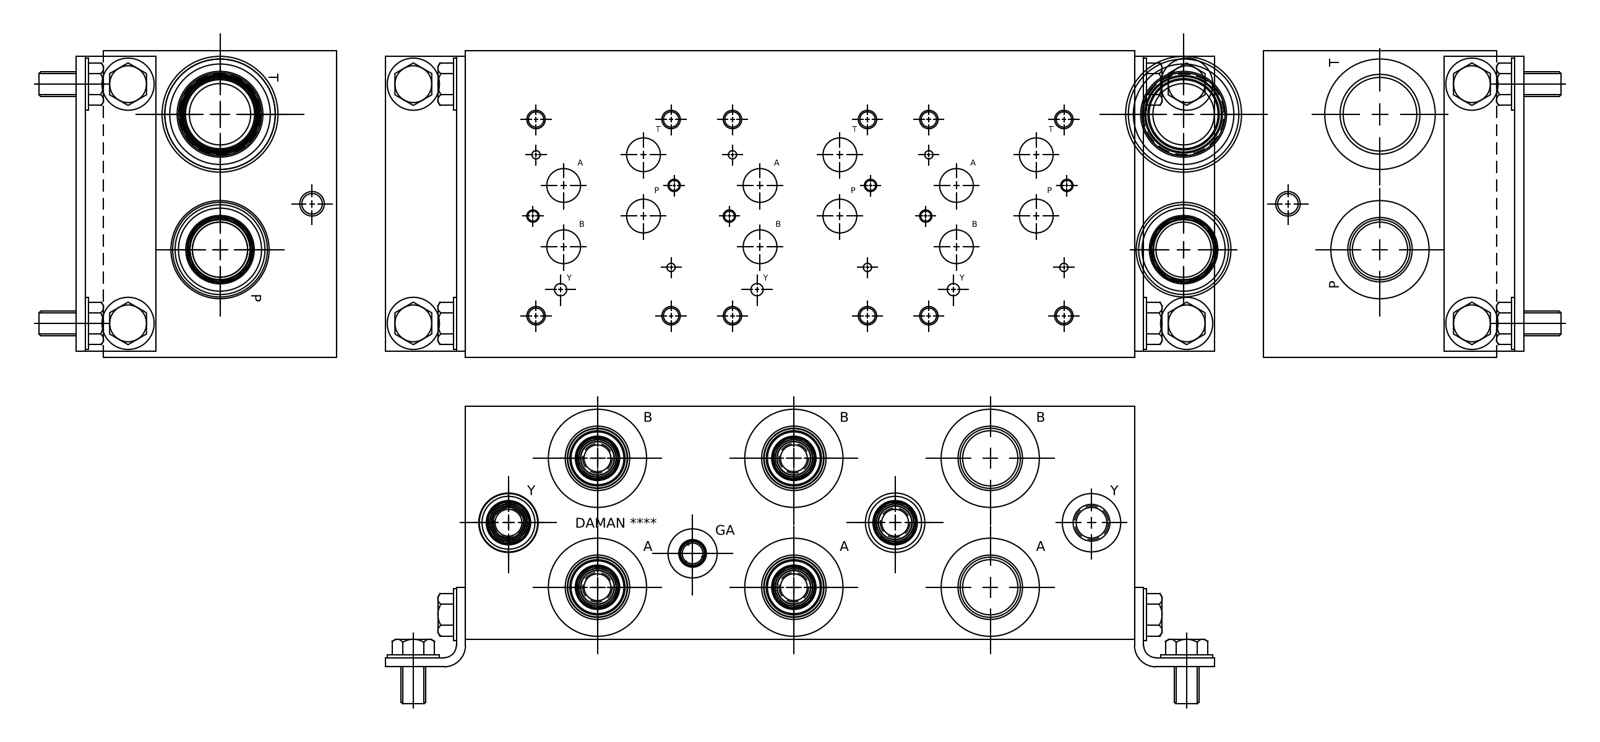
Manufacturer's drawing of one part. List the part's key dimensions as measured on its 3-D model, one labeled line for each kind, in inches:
Part name (STEP PRODUCT): Part_AD07HP034S_3D
STEP written by: Autodesk Inventor 2020 (AUTOMOTIVE_DESIGN)
Units: inches
Bodies: 1 solid, 844 faces (440 planar, 140 cylindrical, 264 other)
Overall size (bounding box): 13.625 × 6.25 × 4.75
Volume: 378.5 in³ · Surface area: 462.4 in²
Round holes (diameter × count): ⌀0.75 ×14, ⌀0.312 ×12, ⌀0.375 ×12, ⌀1.063 ×7, ⌀1.231 ×7, ⌀1.329 ×7, ⌀1.934 ×7, ⌀0.171 ×6, ⌀0.201 ×6, ⌀0.25 ×6, ⌀1.313 ×6, ⌀1.398 ×6
Main face-to-face distances: 4.75, 6.25, 13.625, 0.031, 6.219, 13.594, 13.594, 13.563, 0.031, 0.75
Hole centre spacings: 4, 1.25, 4.191, 1.741, 4.667, 4.854, 0.884, 2.25
